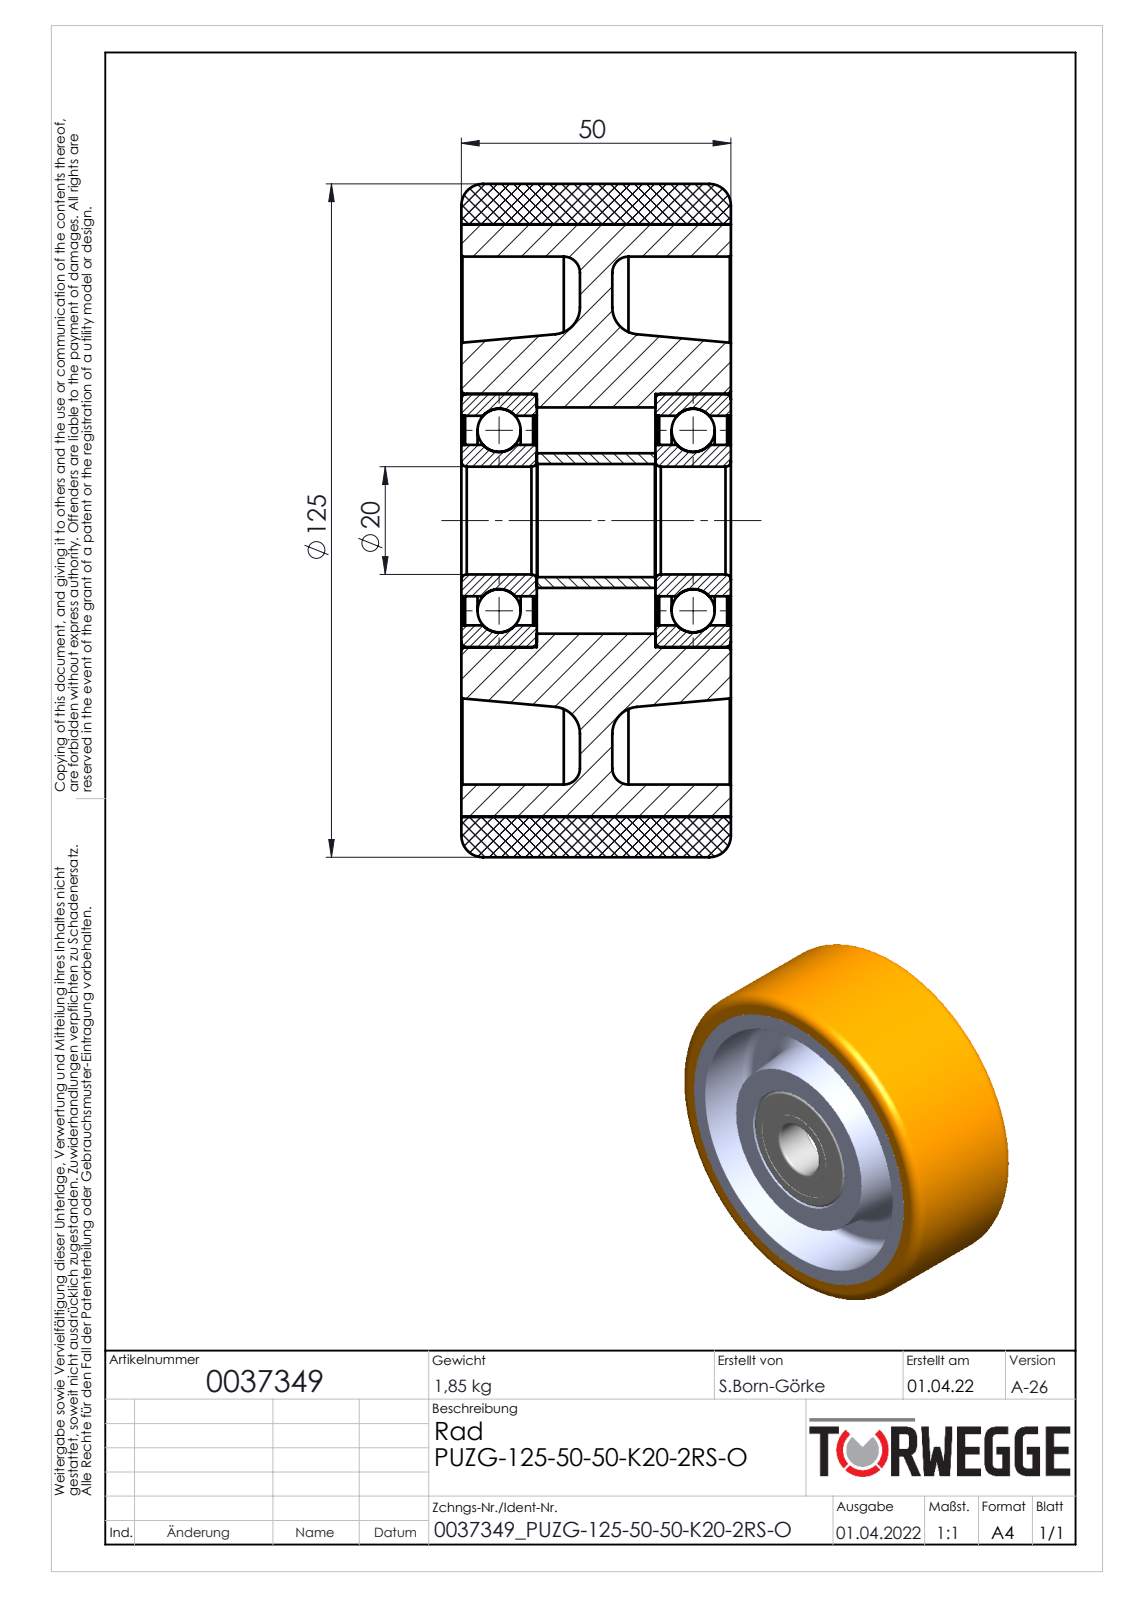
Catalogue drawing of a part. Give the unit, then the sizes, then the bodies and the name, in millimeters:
Units: millimetres
Overall size (bounding box): 125 × 125 × 50
Round holes (diameter × count): ⌀20 ×1, ⌀21 ×1, ⌀28.1 ×1, ⌀38.9 ×1, ⌀42 ×1, ⌀47 ×1, ⌀98 ×1, ⌀110 ×1
Round bosses / shafts (diameter × count): ⌀125 ×1, ⌀25 ×1
Main face-to-face distances: 50, 22, 36, 14, 28, 0.7, 13.3, 13.8, 0.5, 13.1
Volume: 399 114 mm³ · Surface area: 130 937 mm²
Bodies: 13 solids, 160 faces (28 planar, 60 cylindrical, 72 other)
Part name (STEP PRODUCT): 0037349
STEP written by: SolidWorks 2020 (AUTOMOTIVE_DESIGN)
